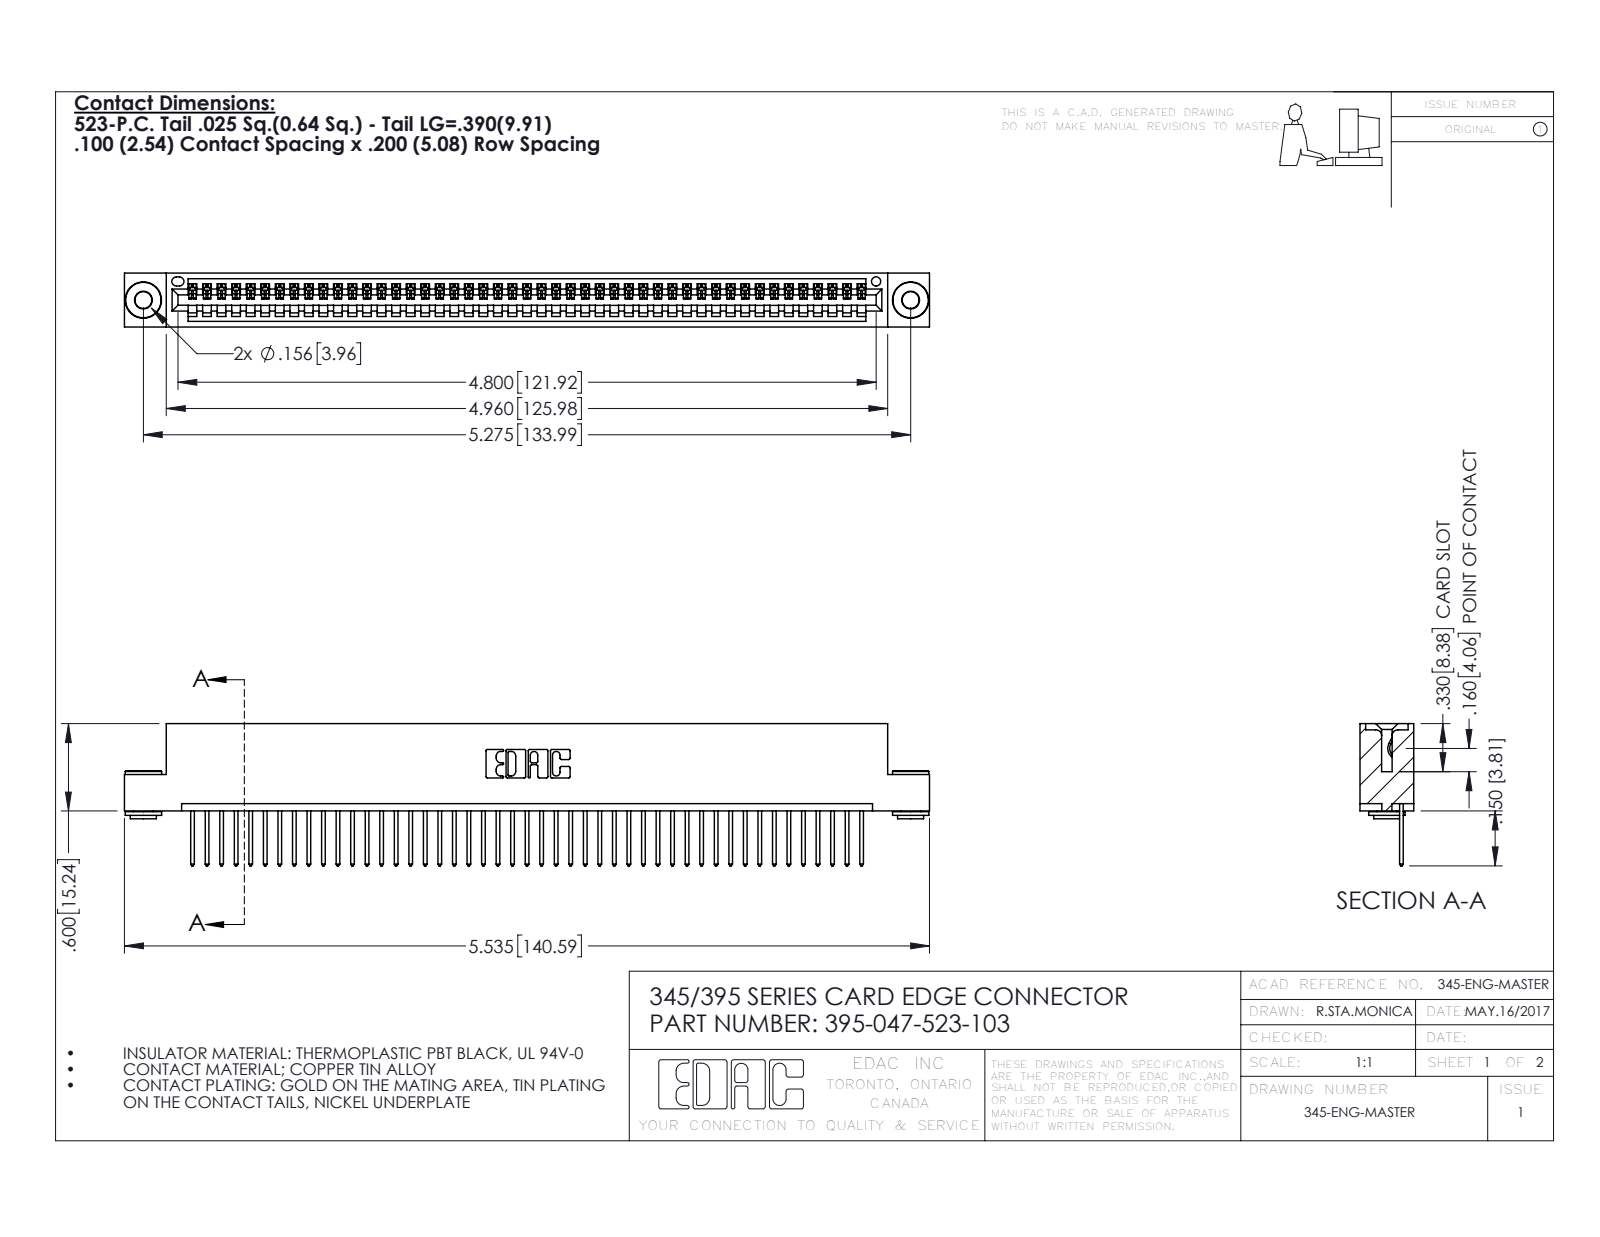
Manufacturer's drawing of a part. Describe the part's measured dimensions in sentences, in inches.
The part is named "395-047-523-103; 345-250-002_345-250-002-102; 345 Part_Flush Mounting Lugs - 0.156 Dia-TH; 345-292-001_345-293-123". Its 3-D file was written by "SolidWorks 2016 (CONFIG_CONTROL_DESIGN)". It is 50 solids with 2890 faces: 1970 planar, 912 cylindrical and 8 other. Overall it measures 5.535 by 0.977 by 0.37 inches. Its volume is 0.817 cubic inches and its surface area 28.11 square inches. Round holes: 2 of diameter 0.116, 2 of diameter 0.156, 1 of diameter 0.064. Round bosses or shafts: 2 of diameter 0.25, 2 of diameter 0.18, 2 of diameter 0.136. Partial cylindrical surfaces (rounded edges, fillets, slot ends): 94 of radius 0.006, 94 of radius 0.01, 22 of radius 0.01, 6 of radius 0.007, 6 of radius 0.031, 3 of radius 0.026, 2 of radius 0.031, 2 of radius 0.04. The main face-to-face distances are 0.072, 0.298, 0.2, 0.37, 0.025, 0.098, 0.272, 0.225, 0.149, 0.072. The hole center spacings are 0.27, 5.039, 5.275.
